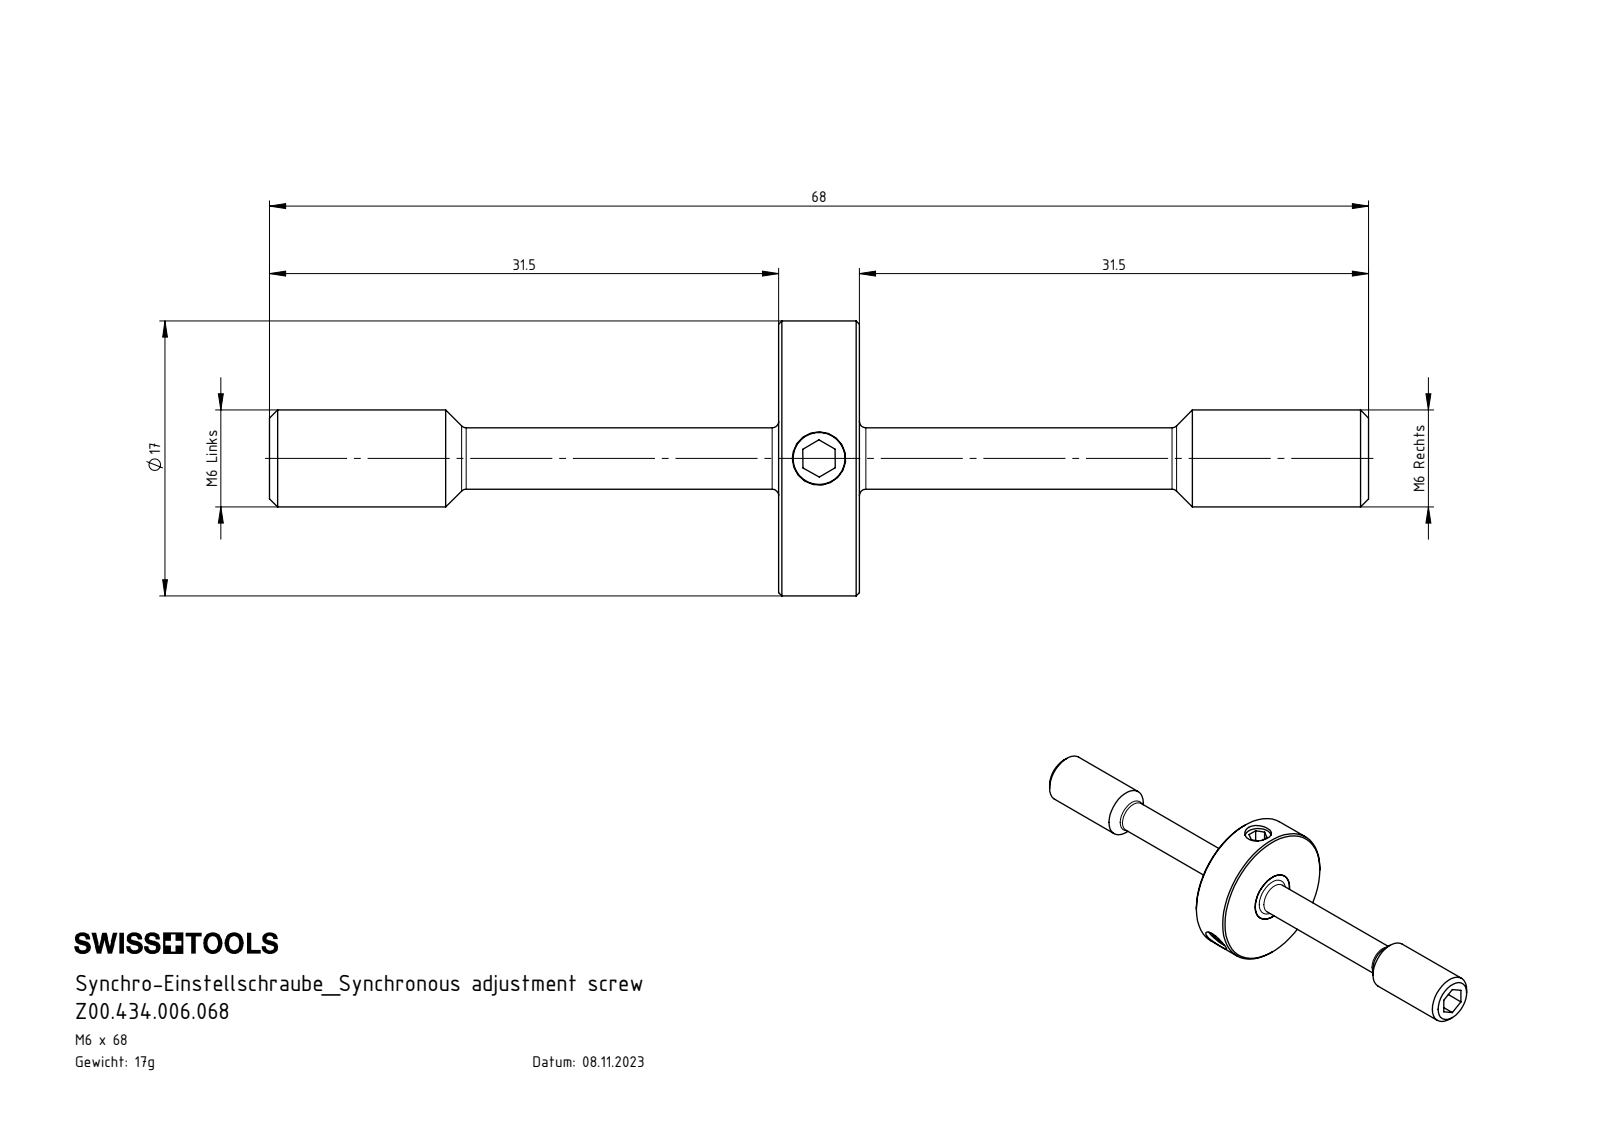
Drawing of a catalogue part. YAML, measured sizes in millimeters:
part_name: "Z72-ER3.001.068_A; ISO 4026 - M4 x 5; Z00.434.006.068; Z42-ER3.002.005_A"
step_written_by: "SolidWorks 2022 (AUTOMOTIVE_DESIGN)"
units: millimeters
bodies: {solids: 5, faces: 99, planar: 39, cylindrical: 26, other: 34}
overall_size: [68, 17, 17]
volume: 2213
surface_area: 2285
round_holes:
  - {diameter: 3.3, count: 3}
round_bosses_or_shafts:
  - {diameter: 4, count: 3}
  - {diameter: 17, count: 1}
  - {diameter: 6, count: 1}
  - {diameter: 3.8, count: 1}
face_to_face_distances: [5, 31.5, 36.5, 2, 2.5, 3, 68, 33, 35, 1.5]
